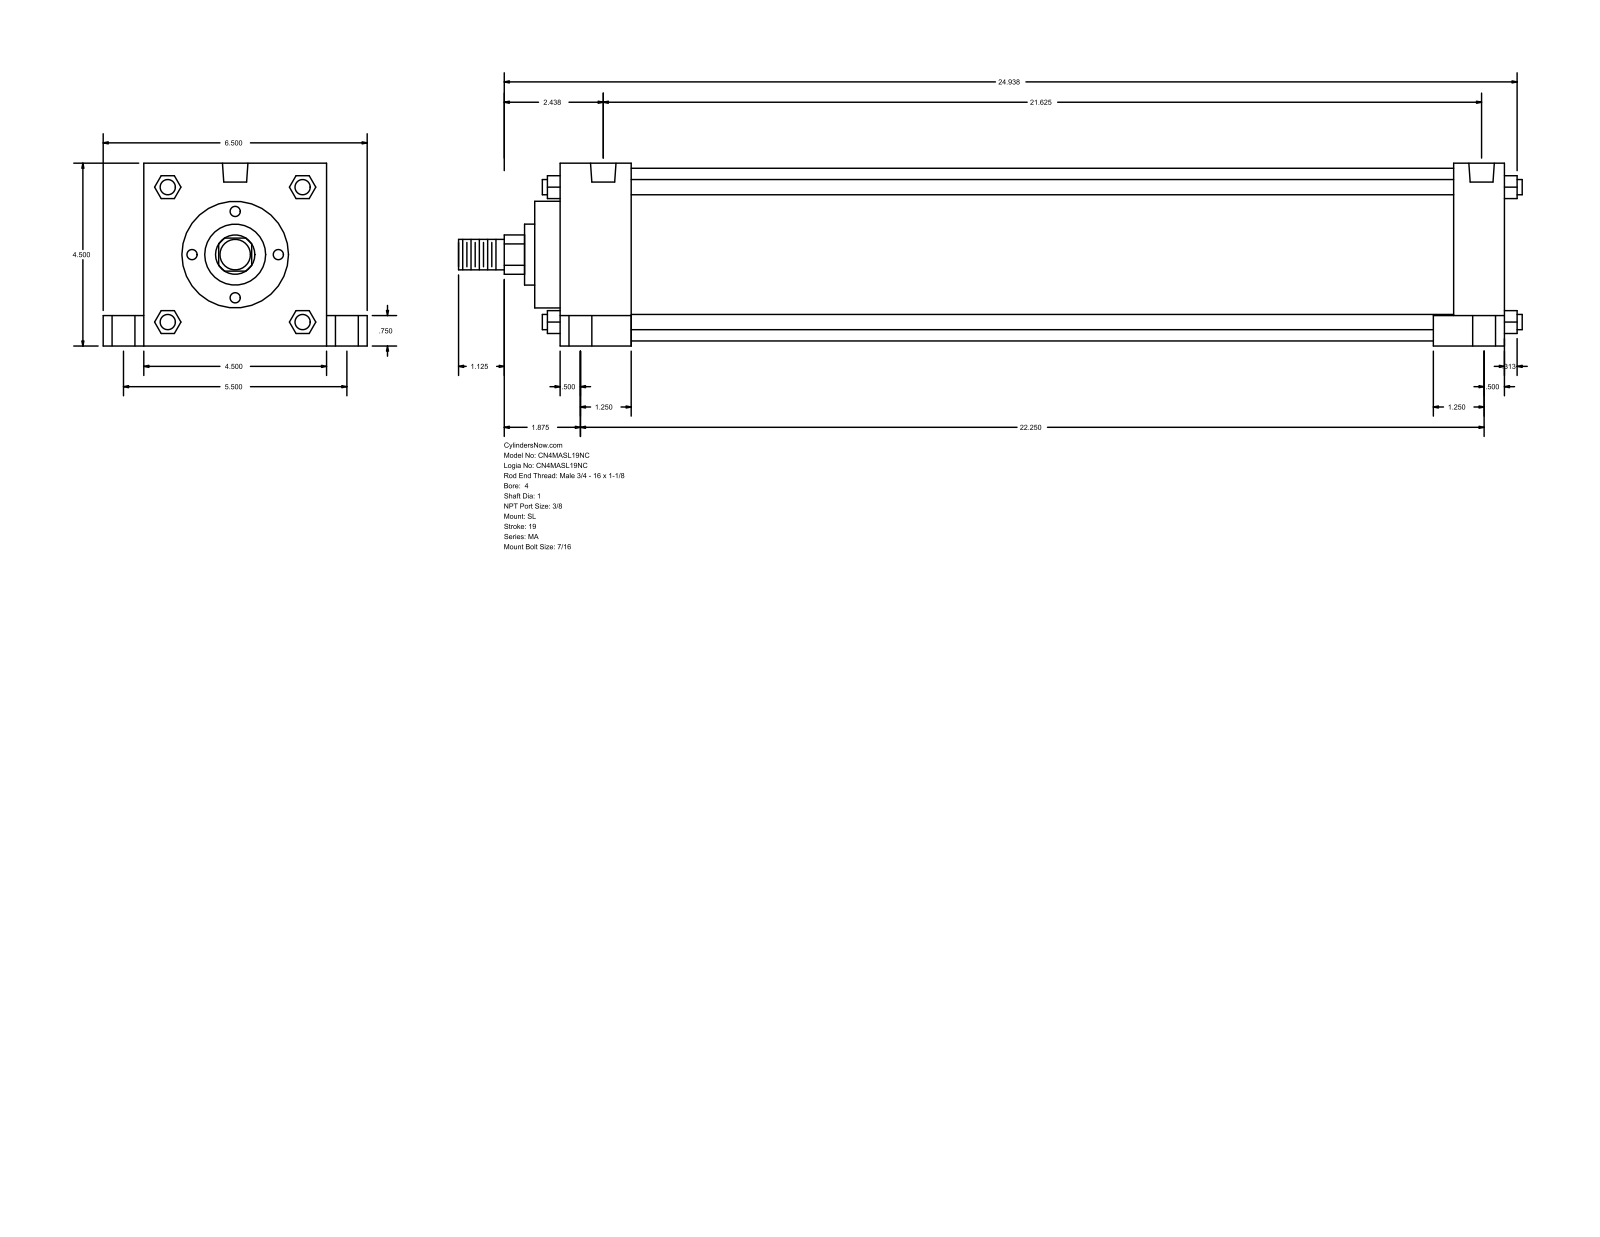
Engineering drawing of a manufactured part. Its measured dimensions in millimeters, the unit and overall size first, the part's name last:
Units: millimetres
Overall size (bounding box): 665.16 × 165.1 × 114.3
Round holes (diameter × count): ⌀11.11 ×4, ⌀14.29 ×4, ⌀20.64 ×4, ⌀15.93 ×2
Round bosses / shafts (diameter × count): ⌀9.53 ×4, ⌀107.95 ×1, ⌀66.67 ×1, ⌀38.1 ×1, ⌀25.4 ×1, ⌀19.05 ×1
Partial cylindrical surfaces — rounded edges, fillets, slot ends (radius × count): R12.29 ×1
Main face-to-face distances: 114.3, 590.56, 514.35, 44.46, 546.1, 558.81, 31.75, 25.4, 139.7, 19.05
Hole centre spacings: 69.87, 70.14, 71.3, 72.4, 139.7, 539.75, 550.55, 555.27
Bodies: 0 solids, 150 faces (113 planar, 37 cylindrical, 0 other)
Part name (STEP PRODUCT): MA_SL__0400_1
STEP written by: GSSL Pune (CONFIG_CONTROL_DESIGN)
